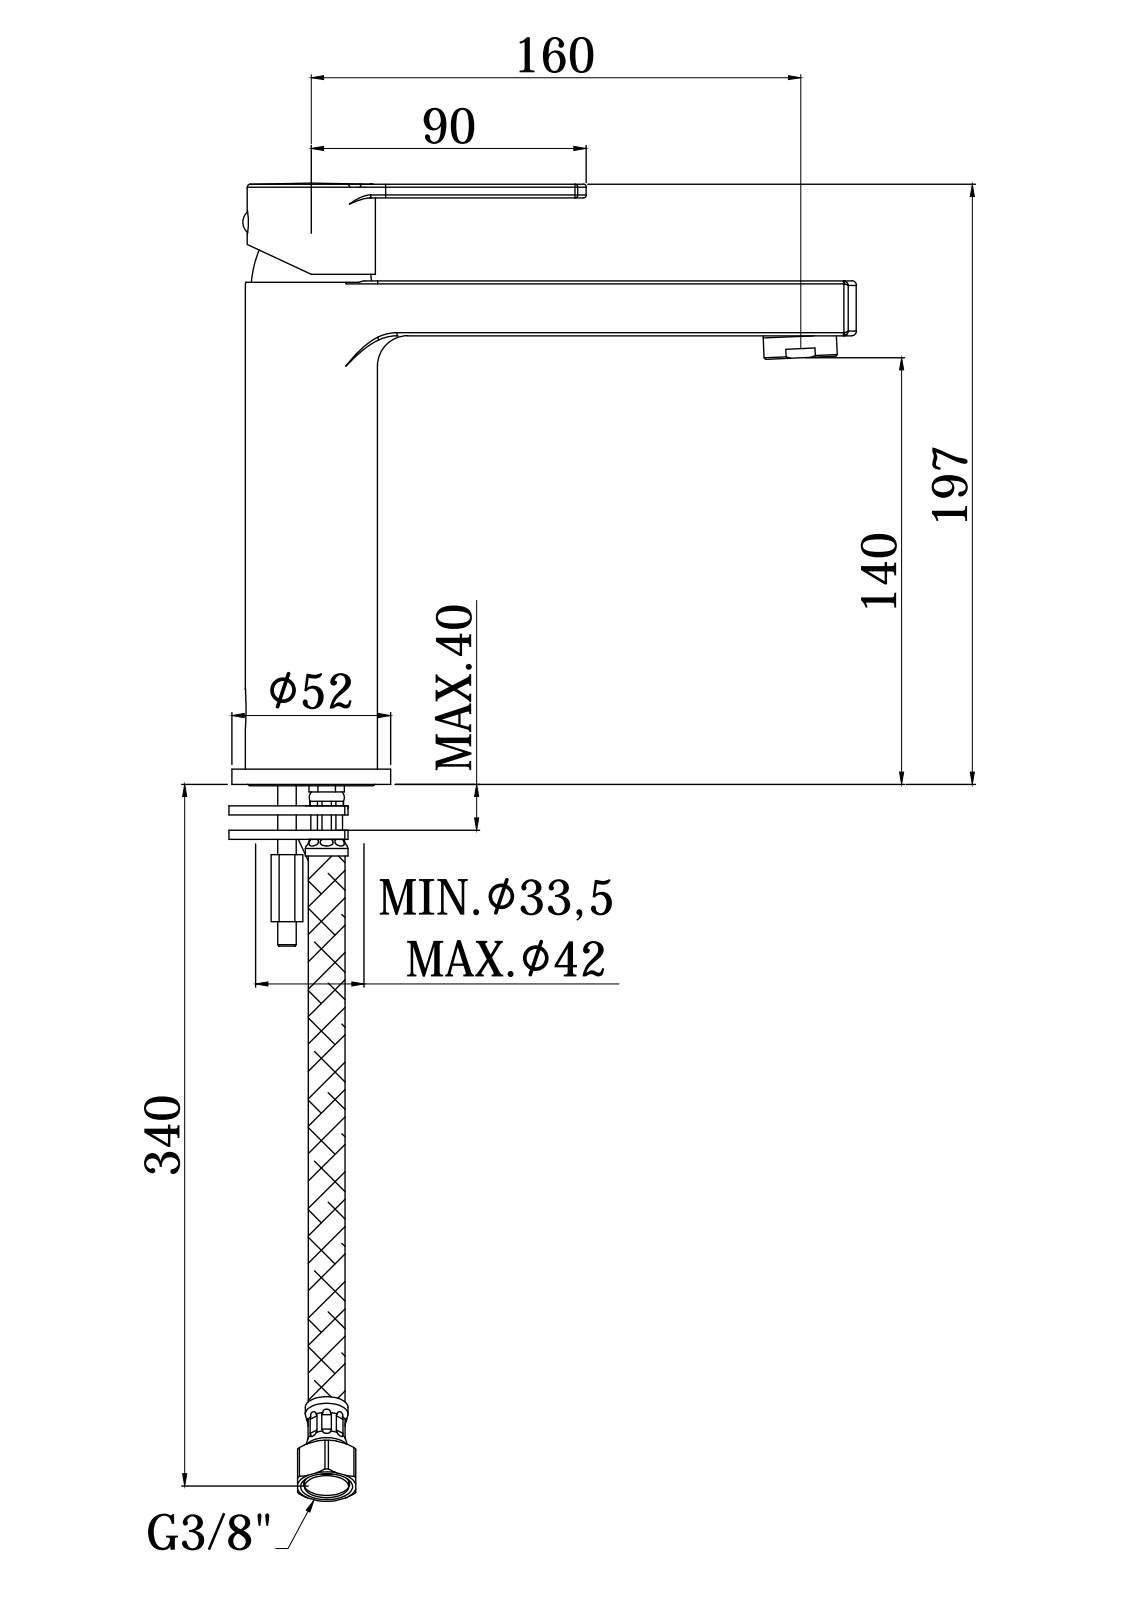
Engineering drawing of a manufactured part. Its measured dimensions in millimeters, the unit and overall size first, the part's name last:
Units: millimetres
Overall size (bounding box): 204 × 196.08 × 52
Round holes (diameter × count): ⌀6 ×4, ⌀8.2 ×4, ⌀5 ×2, ⌀5.5 ×2, ⌀6.5 ×2, ⌀7 ×2, ⌀8 ×2, ⌀9 ×2, ⌀3 ×1, ⌀3.3 ×1, ⌀3.4 ×1, ⌀4 ×1
Round bosses / shafts (diameter × count): ⌀8 ×4, ⌀11 ×2, ⌀4.8 ×2, ⌀4 ×2, ⌀52 ×1, ⌀43.2 ×1, ⌀42.6 ×1, ⌀42 ×1
Partial cylindrical surfaces — rounded edges, fillets, slot ends (radius × count): R0.5 ×44, R1 ×28, R1.5 ×14, R2 ×9, R1.7 ×6, R0.8 ×4, R5.8 ×4, R20 ×4
Main face-to-face distances: 3.5, 14.5, 18, 11, 27.5, 1, 31, 2.5, 24, 29.53
Hole centre spacings: 14, 13.6, 2.83, 8.6, 9.26, 11.77, 13.45, 15.13
Volume: 183 572 mm³ · Surface area: 121 793 mm²
Bodies: 2 solids, 3329 faces (2385 planar, 517 cylindrical, 427 other)
Part name (STEP PRODUCT): RIN074CR
STEP written by: CREO PARAMETRIC BY PTC INC, 2020044 (CONFIG_CONTROL_DESIGN)
